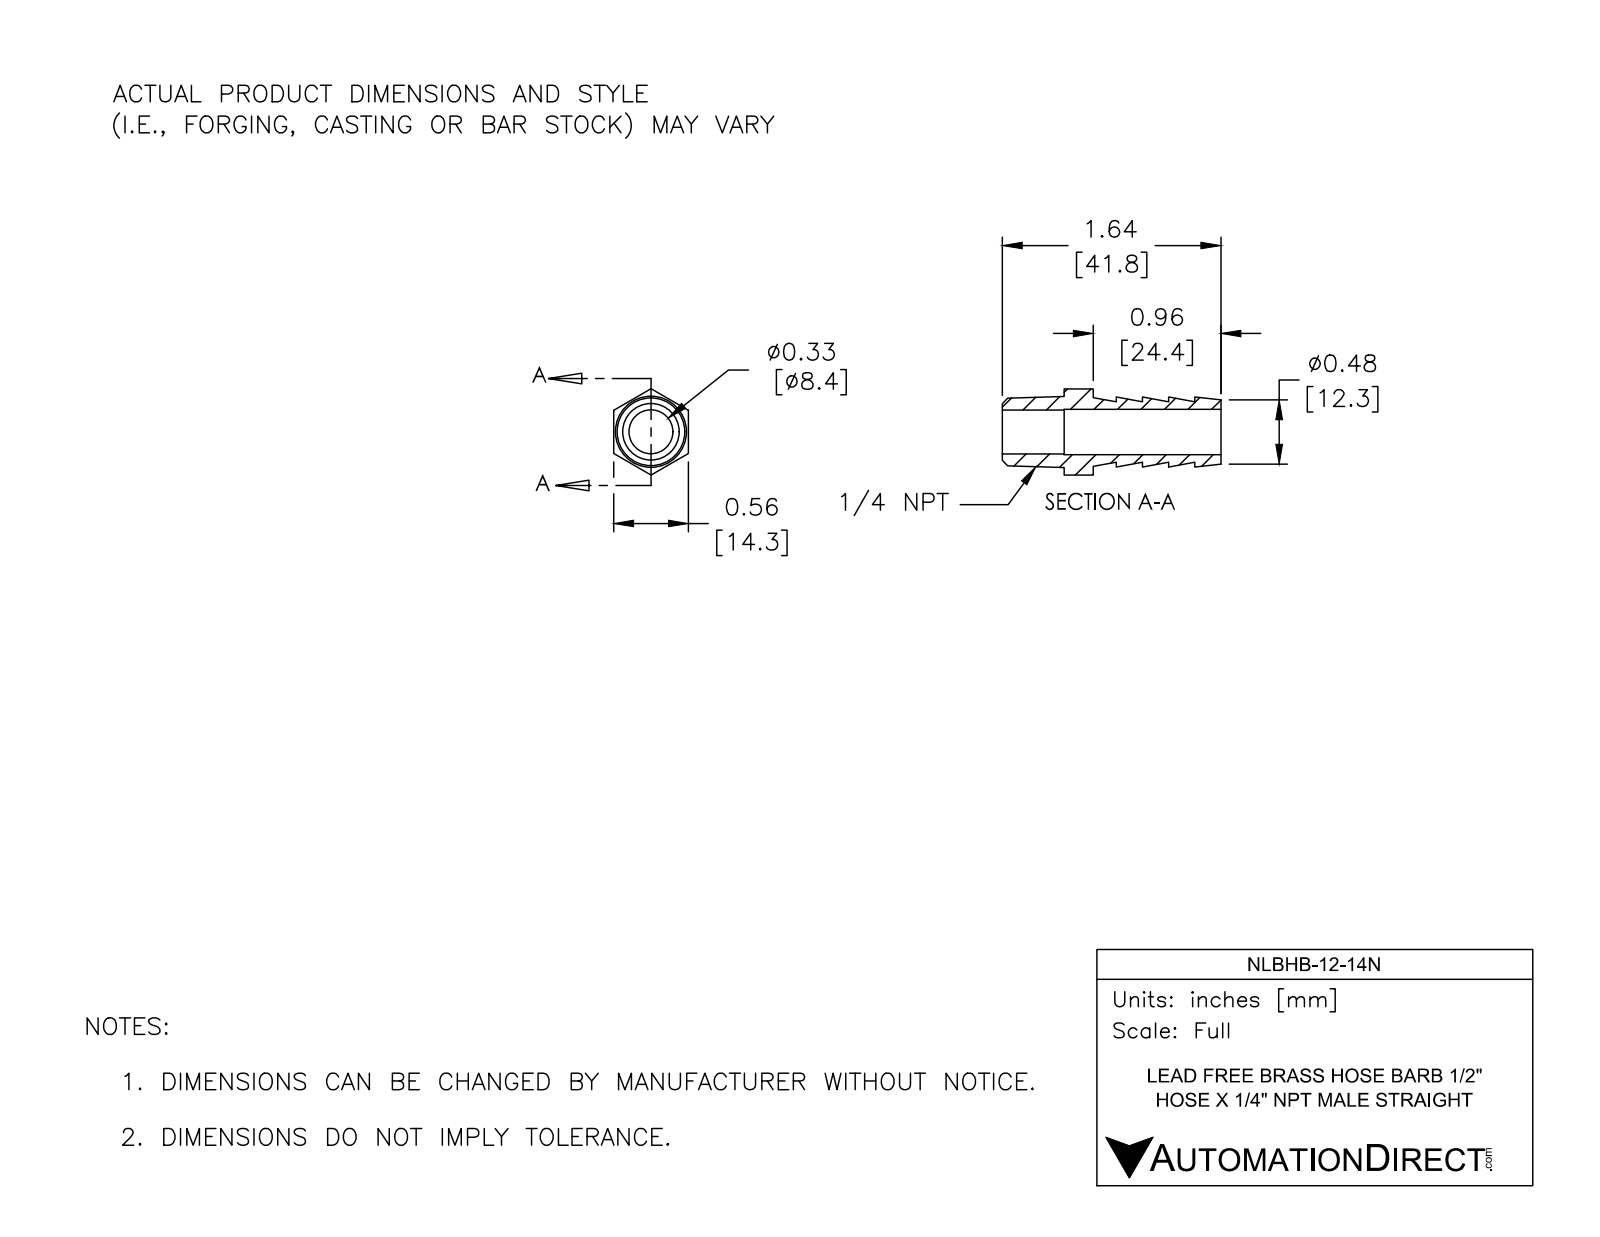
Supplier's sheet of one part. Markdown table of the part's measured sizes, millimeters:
| quantity | value |
| --- | --- |
| part name | NLBHB-12-14N |
| STEP written by | SolidWorks 2017 (AUTOMOTIVE_DESIGN) |
| units | millimeters |
| bodies | 1 solid, 39 faces (15 planar, 10 cylindrical, 14 other) |
| overall size | 41.8 × 16.5 × 14.5 |
| volume | 3 180 mm³ |
| surface area | 3 187 mm² |
| round holes (diameter × count) | 8.4 × 1, 8.6 × 1 |
| partial cylindrical surfaces (radius × count) | 0.8 × 6 |
| main face-to-face distances | 14.5, 5, 10, 15, 5, 24.4, 30, 5.6, 41.8, 17.4 |
